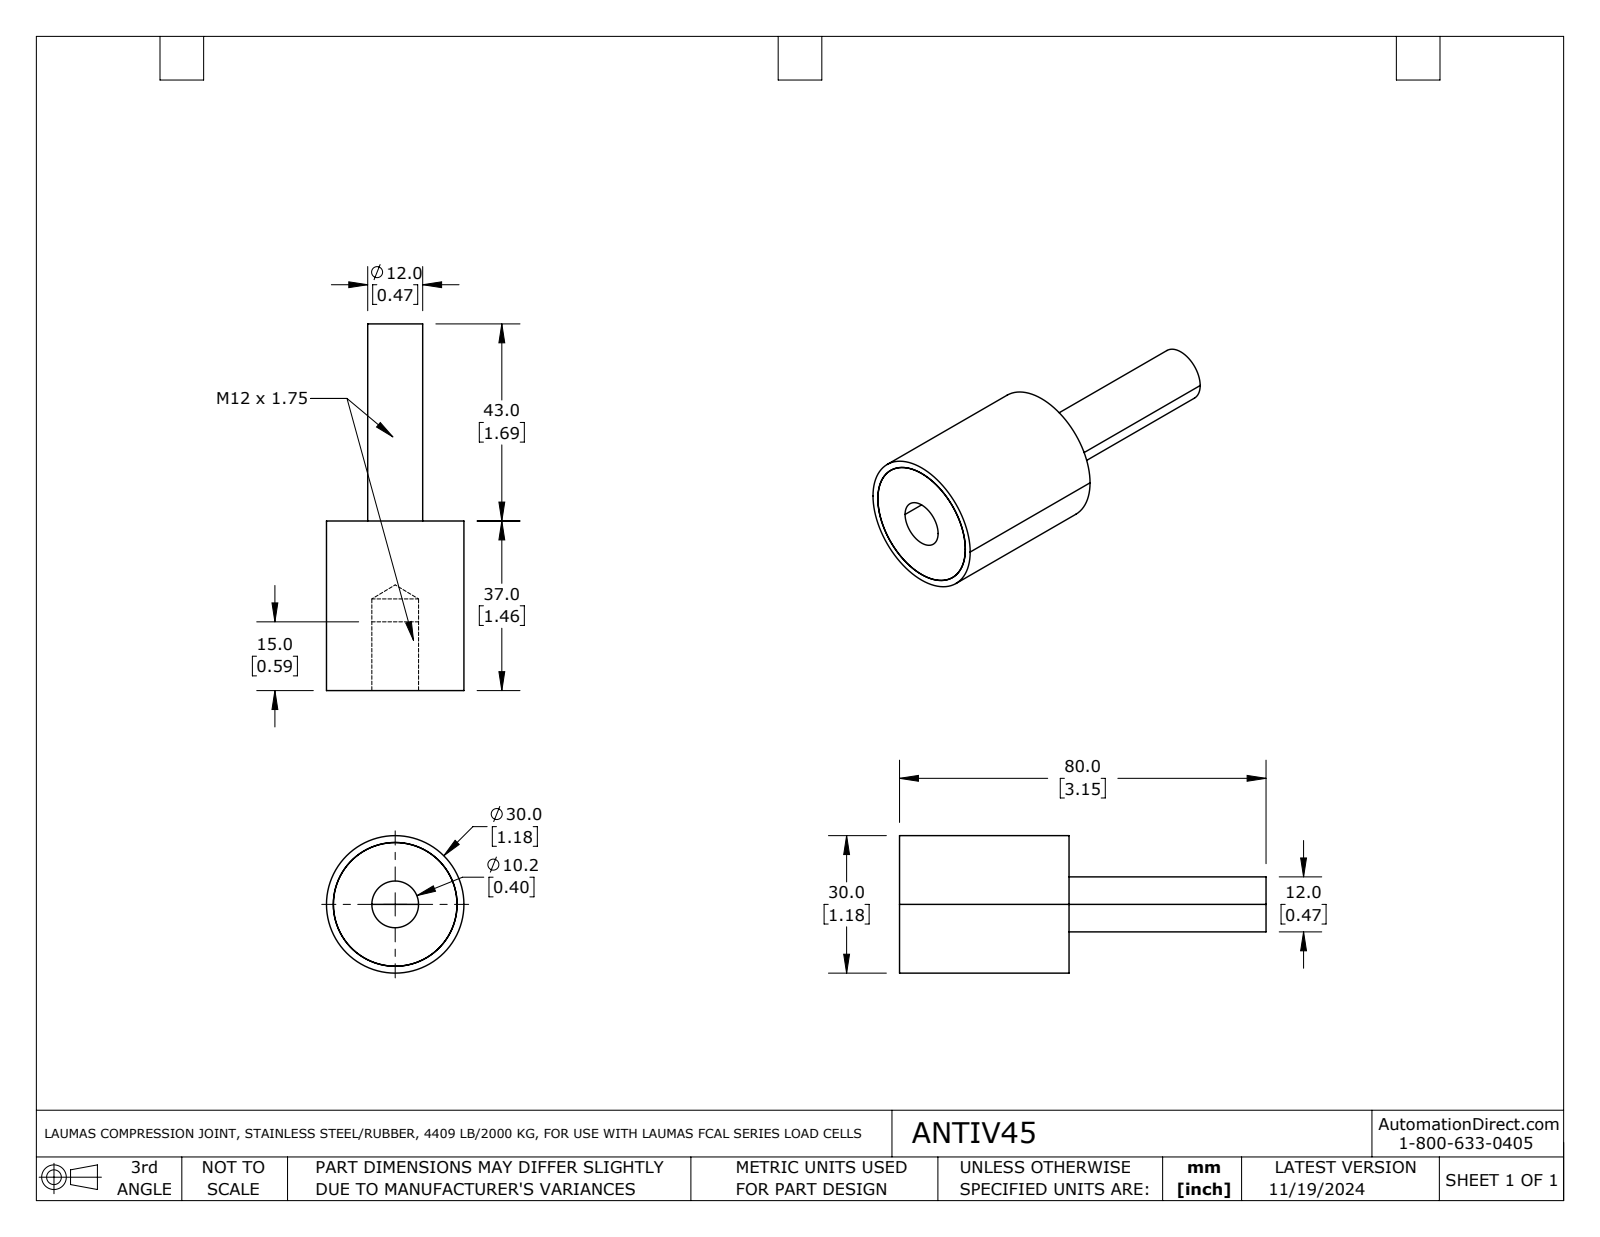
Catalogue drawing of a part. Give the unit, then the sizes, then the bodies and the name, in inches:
Units: inches
Overall size (bounding box): 3.15 × 1.181 × 1.181
Round holes (diameter × count): ⌀0.402 ×1, ⌀1.063 ×1
Round bosses / shafts (diameter × count): ⌀1.181 ×1, ⌀0.472 ×1
Main face-to-face distances: 1.457, 1.693, 3.15
Volume: 1.788 in³ · Surface area: 20.85 in²
Bodies: 2 solids, 18 faces (5 planar, 10 cylindrical, 3 other)
Part name (STEP PRODUCT): ANTIV45
STEP written by: SolidWorks 2021 (AUTOMOTIVE_DESIGN)
